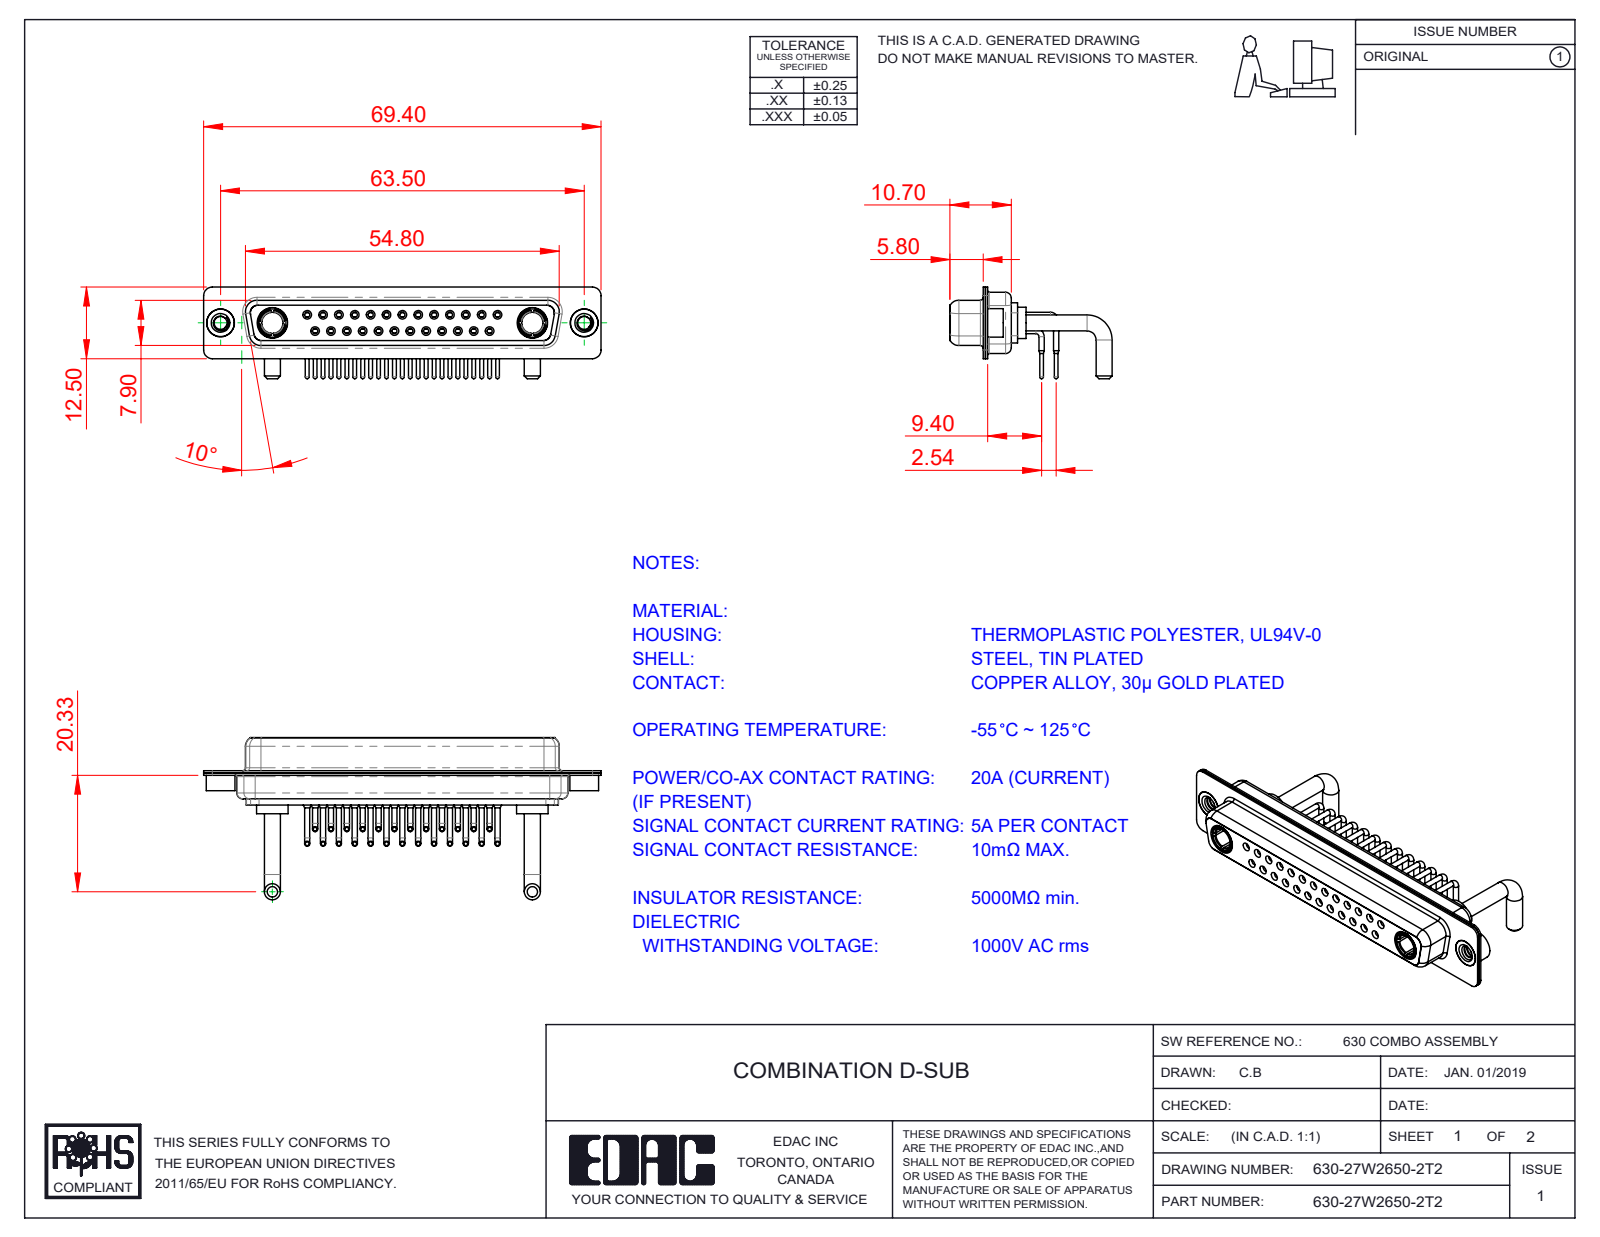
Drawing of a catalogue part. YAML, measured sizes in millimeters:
part_name: "630Combo Contact Row 1; 630Combo Shell Front_37 Contacts; 630-27W2650-2T2; 630Combo Contact Row 2 (+4 more)"
step_written_by: "SolidWorks 2020 (CONFIG_CONTROL_DESIGN)"
units: millimeters
bodies: {solids: 34, faces: 1760, planar: 500, cylindrical: 762, other: 498}
overall_size: [69.4, 28.33, 16]
volume: 5763
surface_area: 12677
round_holes:
  - {diameter: 0.9, count: 25}
  - {diameter: 1.1, count: 25}
  - {diameter: 1.5, count: 25}
  - {diameter: 2, count: 25}
  - {diameter: 1.7, count: 13}
  - {diameter: 1.6, count: 12}
  - {diameter: 4.85, count: 4}
  - {diameter: 2.26, count: 2}
  - {diameter: 3.7, count: 2}
  - {diameter: 4, count: 2}
  - {diameter: 4.05, count: 2}
  - {diameter: 5.3, count: 2}
round_bosses_or_shafts:
  - {diameter: 0.9, count: 26}
  - {diameter: 0.65, count: 25}
  - {diameter: 1.6, count: 14}
  - {diameter: 2.8, count: 4}
  - {diameter: 5.5, count: 2}
  - {diameter: 5.2, count: 2}
  - {diameter: 5, count: 2}
  - {diameter: 4.96, count: 2}
partial_cylinders:
  - {radius: 1.5, count: 16}
  - {radius: 2, count: 12}
  - {radius: 1.35, count: 8}
  - {radius: 1.6, count: 8}
  - {radius: 0.25, count: 4}
  - {radius: 0.5, count: 4}
  - {radius: 0.6, count: 4}
  - {radius: 0.65, count: 4}
face_to_face_distances: [0.4, 1.4, 0.45, 8.45, 1.8, 8.9, 6.2, 7.05, 1.85, 7.5]
hole_center_spacings: [3.16, 2.77, 5.54, 8.31, 5.03, 7.48, 11.08, 5.04]
